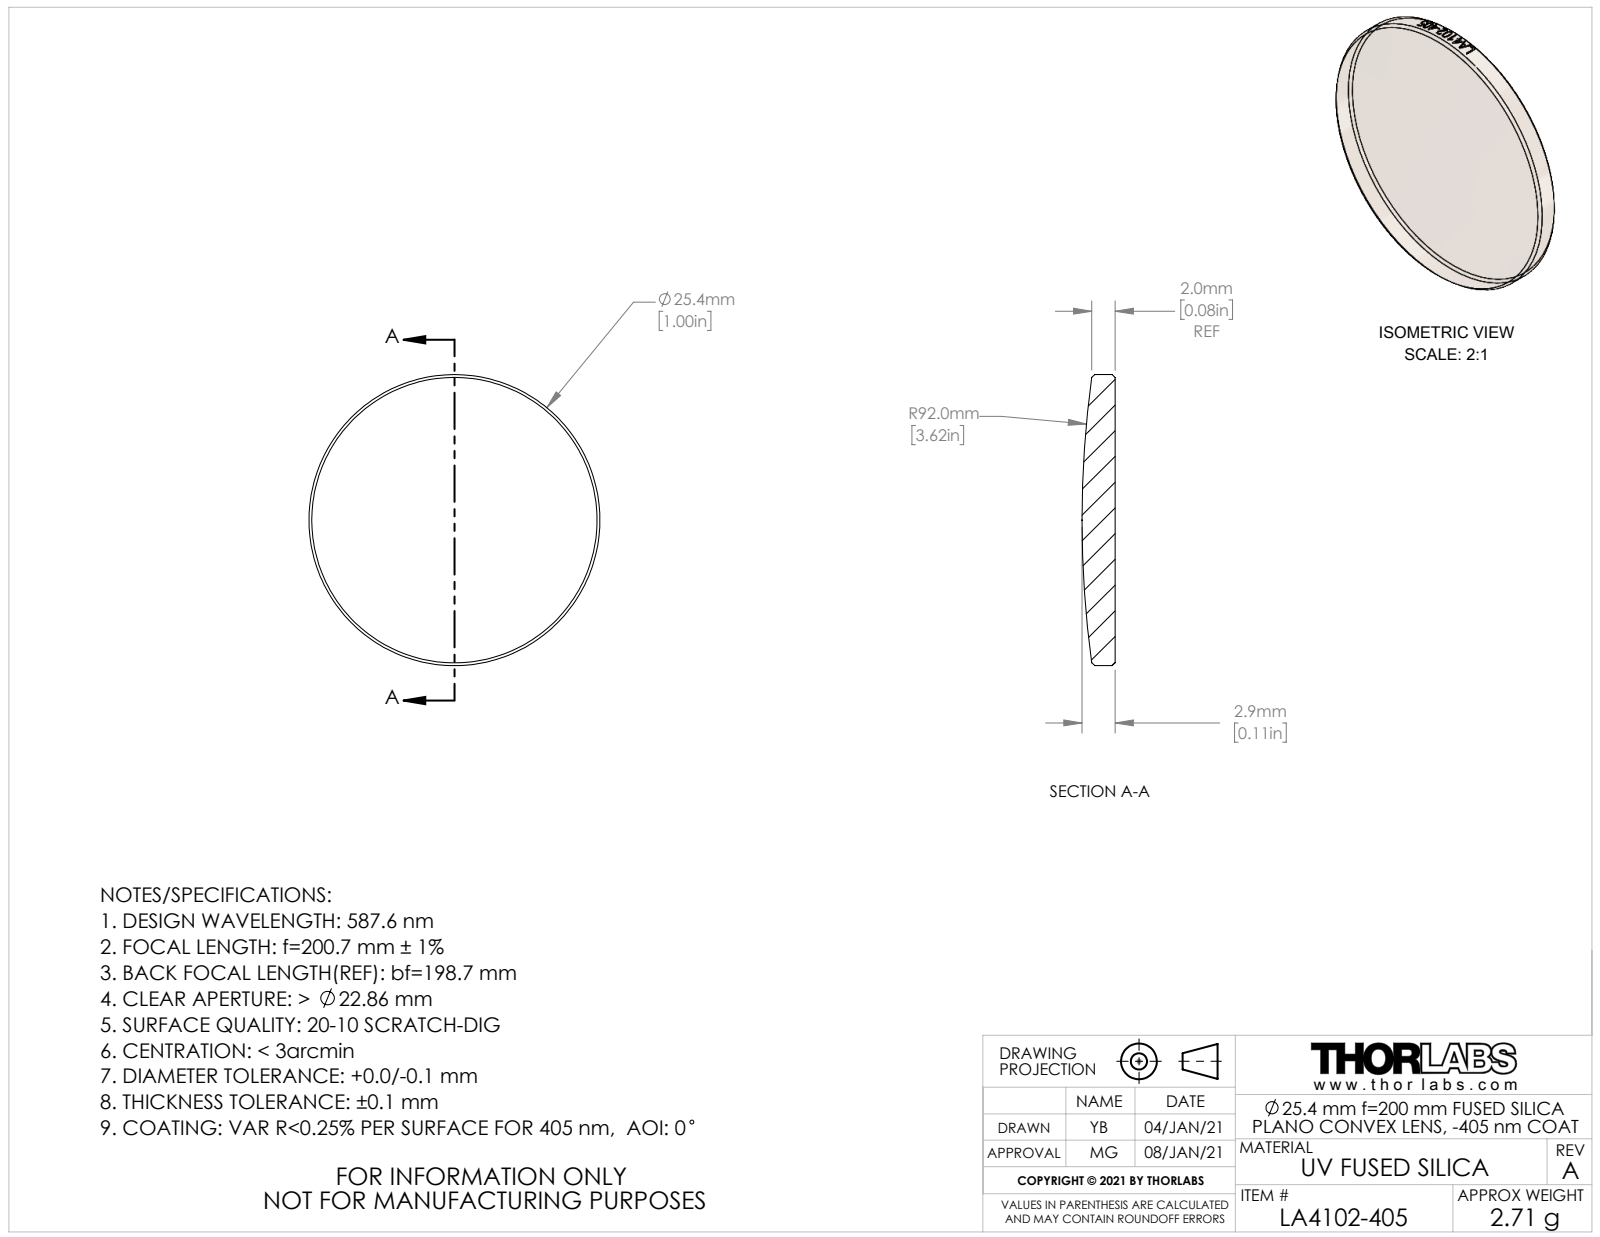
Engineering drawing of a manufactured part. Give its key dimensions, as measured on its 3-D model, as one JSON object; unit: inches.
{"part_name": "CTN016847; CTN016827-E0W", "step_written_by": "SolidWorks 2018 (AUTOMOTIVE_DESIGN)", "units": "inches", "bodies": {"solids": 1, "faces": 26, "planar": 1, "cylindrical": 19, "other": 6}, "overall_size": [1, 1, 0.113], "volume_in3": 0.075, "surface_area_in2": 1.788, "round_bosses_or_shafts": [[1, 1]]}
